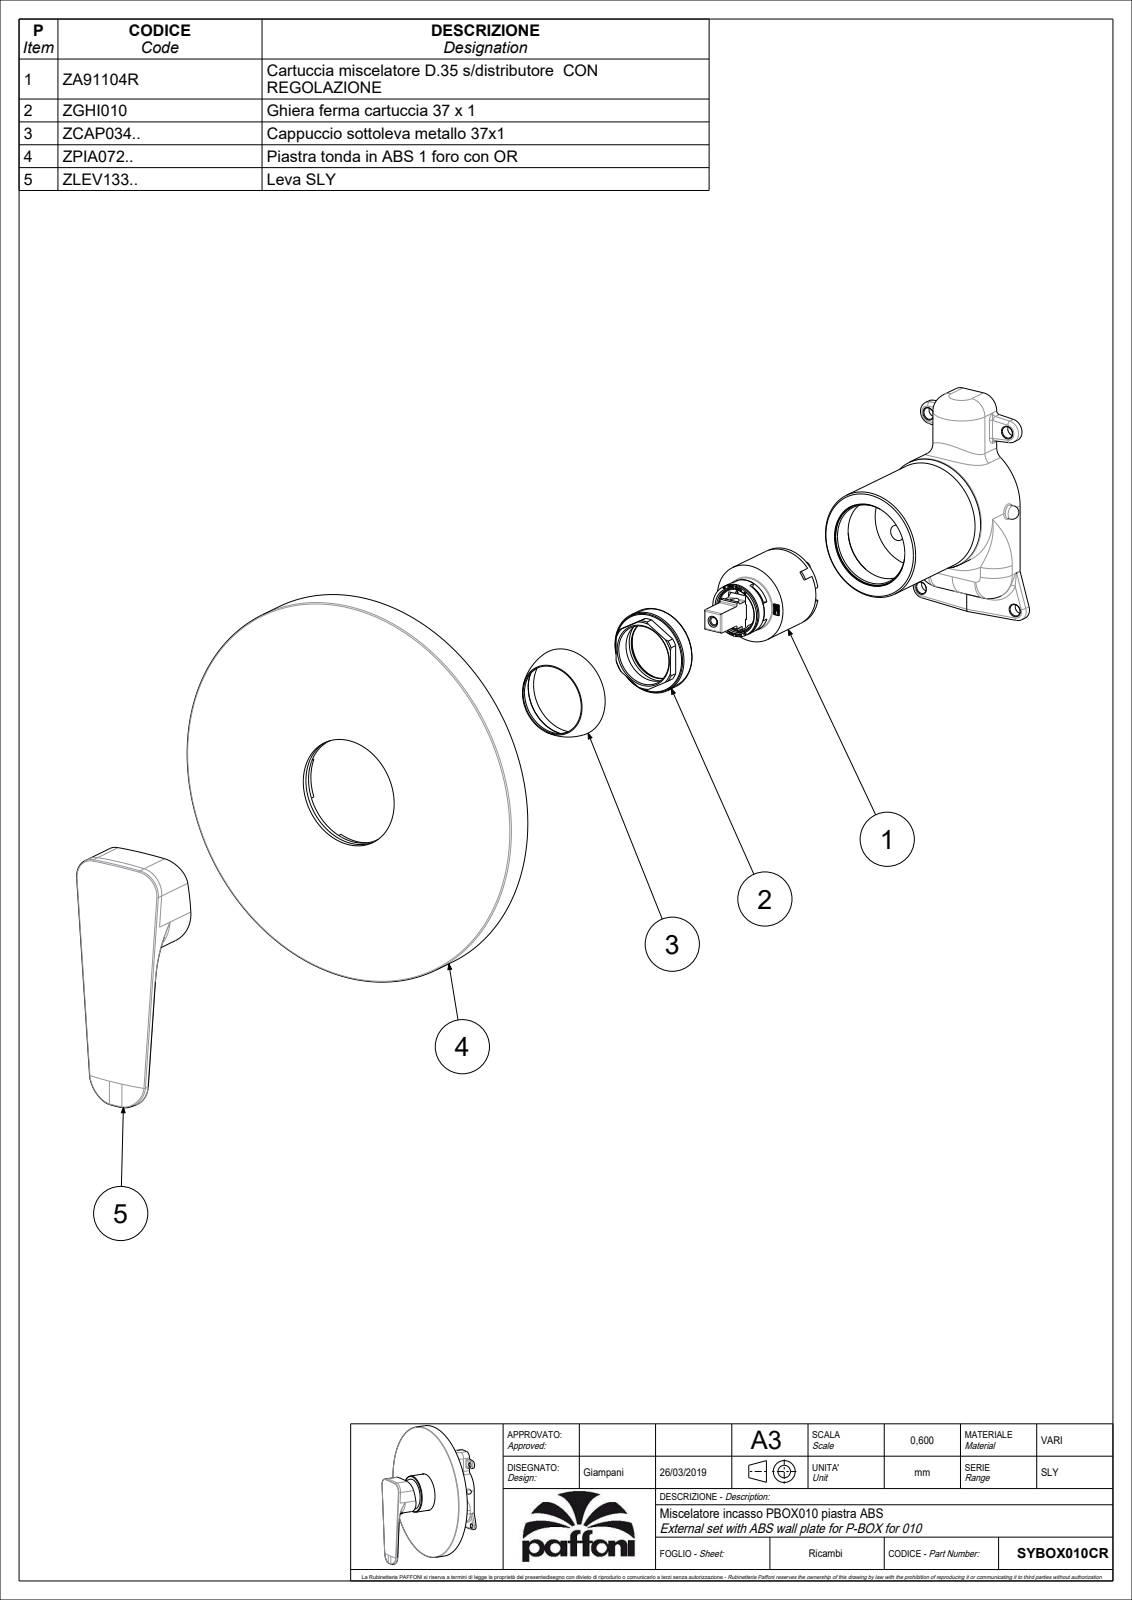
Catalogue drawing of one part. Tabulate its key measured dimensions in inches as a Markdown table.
| quantity | value |
| --- | --- |
| part name | SYBOX010CR |
| STEP written by | CREO PARAMETRIC BY PTC INC, 2020044 (CONFIG_CONTROL_DESIGN) |
| units | inches |
| bodies | 2 solids, 1027 faces (606 planar, 250 cylindrical, 171 other) |
| overall size | 6.949 × 6.811 × 2.673 |
| volume | 14.26 in³ |
| surface area | 162.9 in² |
| round holes (diameter × count) | 0.197 × 3, 0.276 × 3, 0.079 × 2, 0.13 × 2, 0.157 × 2, 0.118 × 1, 0.177 × 1, 0.768 × 1, 0.783 × 1, 1.055 × 1, 1.142 × 1, 1.22 × 1 |
| round bosses / shafts (diameter × count) | 0.189 × 2, 6.811 × 1, 6.575 × 1, 2.224 × 1, 1.894 × 1, 1.535 × 1, 1.378 × 1, 1.37 × 1 |
| partial cylindrical surfaces (radius × count) | 0.02 × 27, 0.006 × 11, 0.012 × 4, 0.059 × 4, 0.039 × 2, 0.394 × 2, 0.098 × 1, 0.177 × 1 |
| main face-to-face distances | 0.512, 0.079, 0.433, 2.496, 2.063, 1.984, 0.177, 0.256, 0.354, 0.268 |
| hole center spacings | 0.339, 0.53, 0.596, 0.863, 0.433, 0.551, 0.709 |
